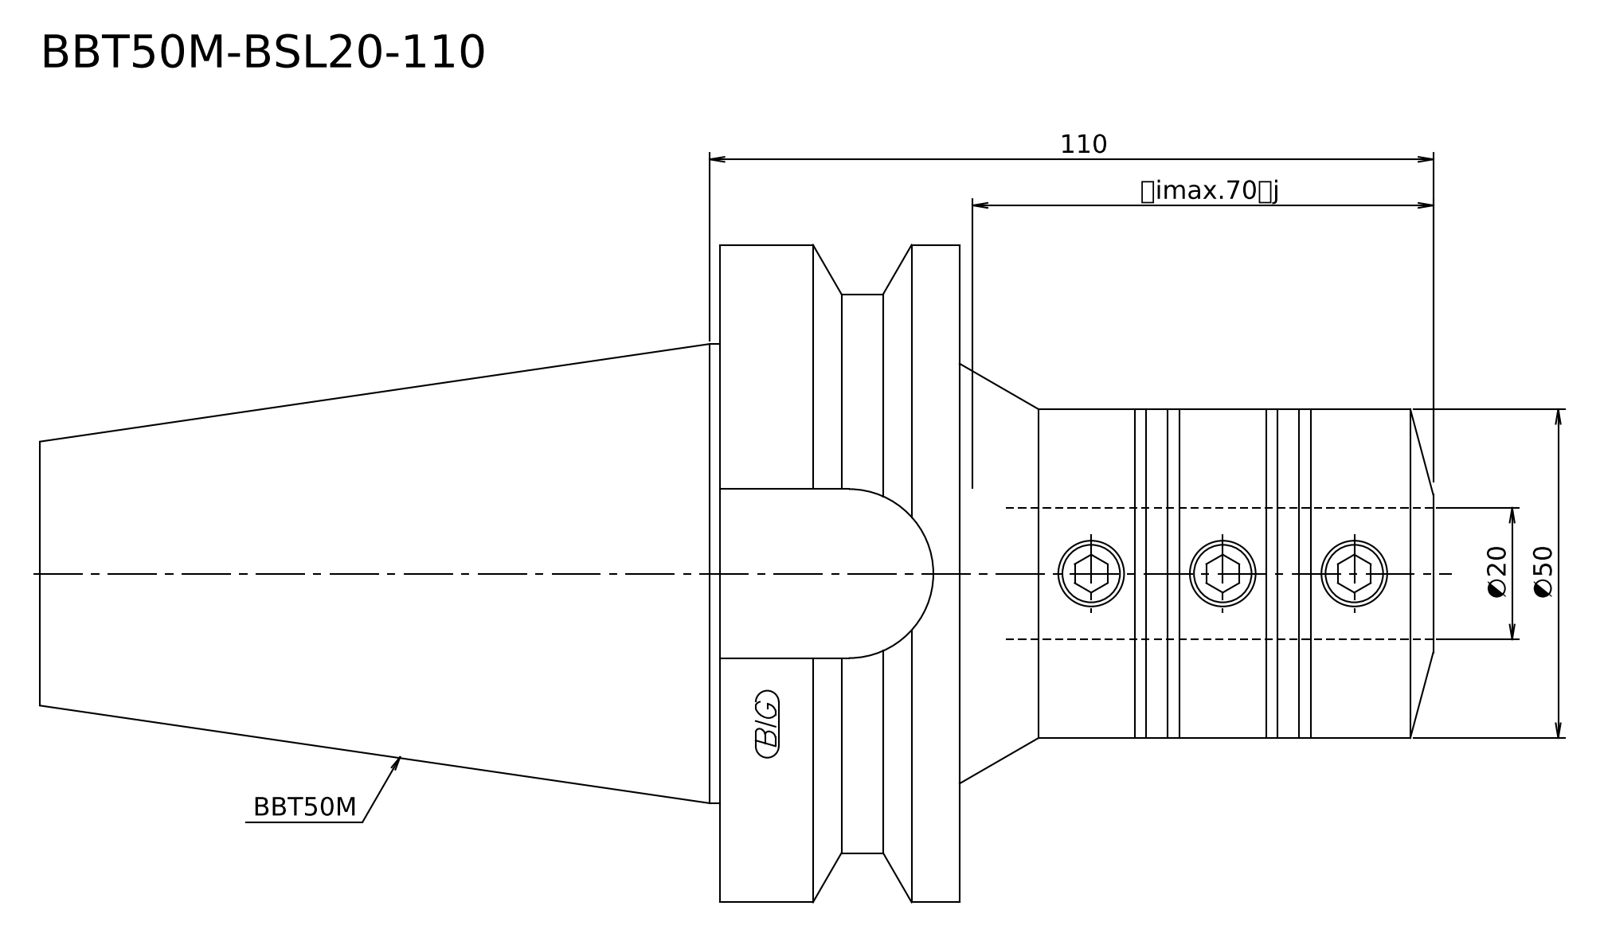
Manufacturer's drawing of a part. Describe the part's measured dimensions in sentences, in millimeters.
Its 3-D file was written by "Kubotek KeyCreator 2011 V10.0.2 (22737) (automotive_design)". It is 1 solid with 14 faces: 4 planar, 5 cylindrical and 5 other. Overall it measures 211.8 by 100 by 100 millimeters. Its volume is 662 243 cubic millimeters and its surface area 54 900 square millimeters. Round bosses or shafts: 1 of diameter 100, 1 of diameter 85, 1 of diameter 69.85, 1 of diameter 50. The main face-to-face distances are 36.5, 139.8, 103.3, 72, 108.5, 211.8.
